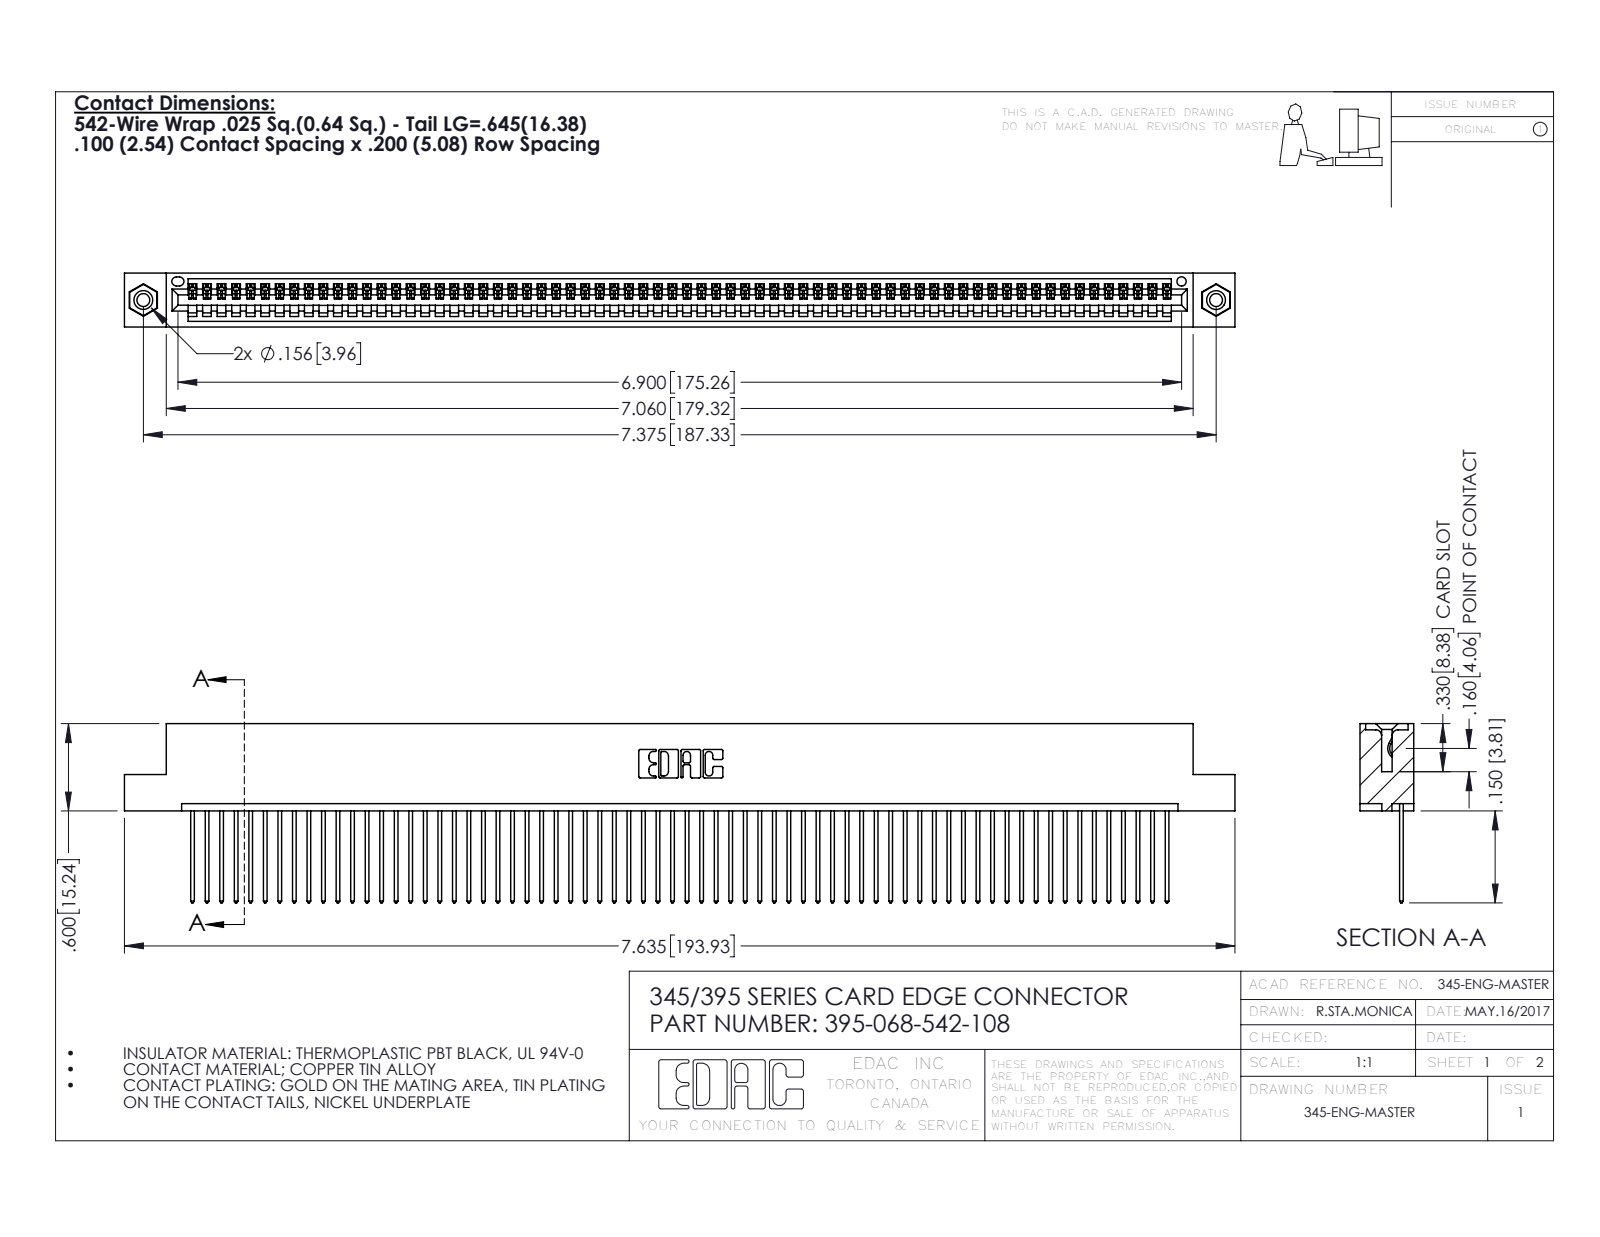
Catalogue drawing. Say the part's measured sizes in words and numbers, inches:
The part is named "345-250-001_345-250-003-102; 345-292-001_345-293-142; 345 Part_Flush Mounting Lugs - 0.156 Dia-TI; 395-068-542-108". Its 3-D file was written by "SolidWorks 2016 (CONFIG_CONTROL_DESIGN)". It is 71 solids with 4130 faces: 2832 planar, 1282 cylindrical and 16 other. Overall it measures 7.635 by 1.232 by 0.37 inches. Its volume is 1.146 cubic inches and its surface area 40.74 square inches. Round holes: 2 of diameter 0.089, 2 of diameter 0.125, 2 of diameter 0.156, 1 of diameter 0.064. Round bosses or shafts: 2 of diameter 0.155. Partial cylindrical surfaces (rounded edges, fillets, slot ends): 136 of radius 0.006, 136 of radius 0.01, 22 of radius 0.01, 6 of radius 0.007, 6 of radius 0.031, 3 of radius 0.026, 2 of radius 0.031, 2 of radius 0.04. The main face-to-face distances are 0.072, 0.298, 0.098, 0.272, 0.025, 0.37, 0.2, 0.225, 0.149, 0.072. The hole center spacings are 0.27, 7.139, 7.375.
